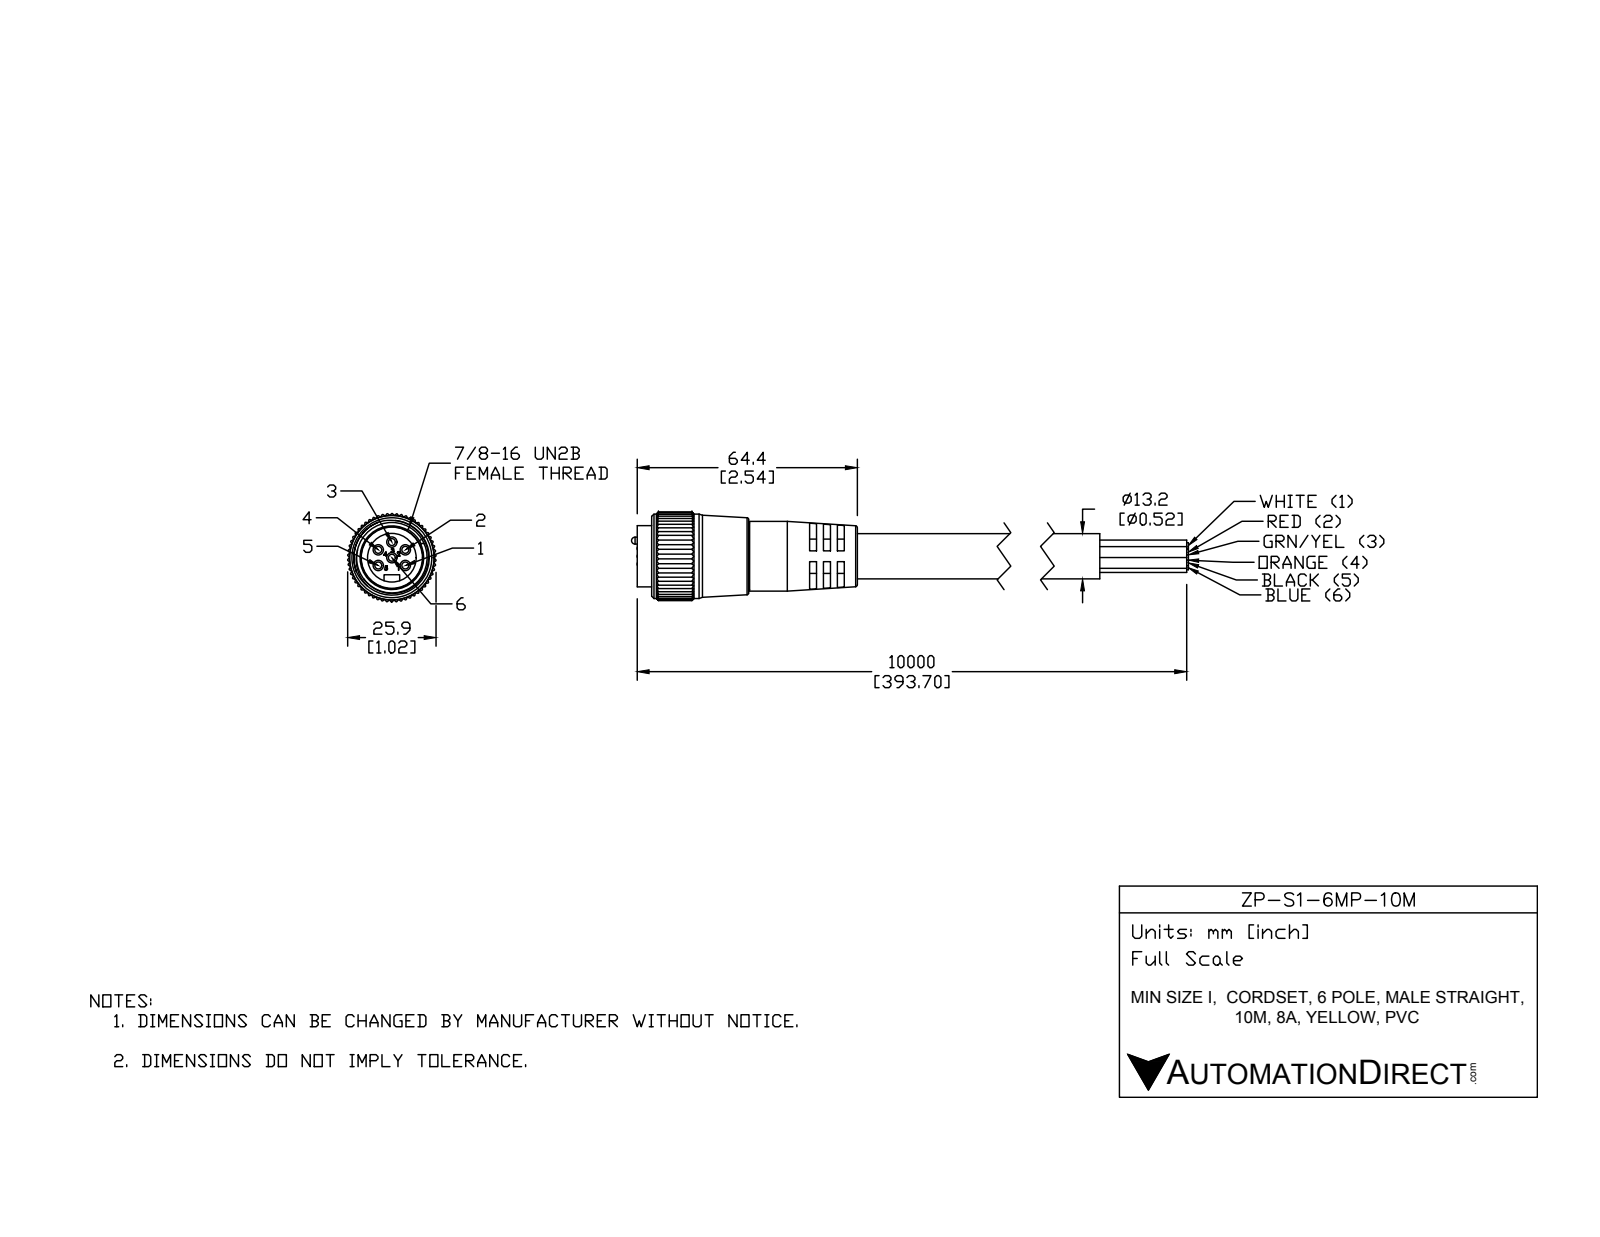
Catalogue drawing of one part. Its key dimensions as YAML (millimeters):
part_name: "ZP-S1-6MP-10M"
step_written_by: "SolidWorks 2015 (AUTOMOTIVE_DESIGN)"
units: millimeters
bodies: {solids: 8, faces: 638, planar: 229, cylindrical: 326, other: 83}
overall_size: [111.28, 52.91, 25.84]
volume: 31376
surface_area: 13508
round_holes:
  - {diameter: 14.22, count: 1}
  - {diameter: 19.96, count: 1}
  - {diameter: 20.45, count: 1}
  - {diameter: 21, count: 1}
round_bosses_or_shafts:
  - {diameter: 3.05, count: 6}
  - {diameter: 2, count: 6}
  - {diameter: 13.21, count: 2}
  - {diameter: 24.68, count: 1}
  - {diameter: 20.4, count: 1}
  - {diameter: 19.5, count: 1}
  - {diameter: 17.88, count: 1}
partial_cylinders:
  - {radius: 0.25, count: 165}
  - {radius: 2.29, count: 1}
  - {radius: 5.25, count: 1}
  - {radius: 12.93, count: 1}
face_to_face_distances: [2, 4.04, 2.04, 6.04, 2.02, 8.06, 6.06, 4.02, 4.03, 10.07]
